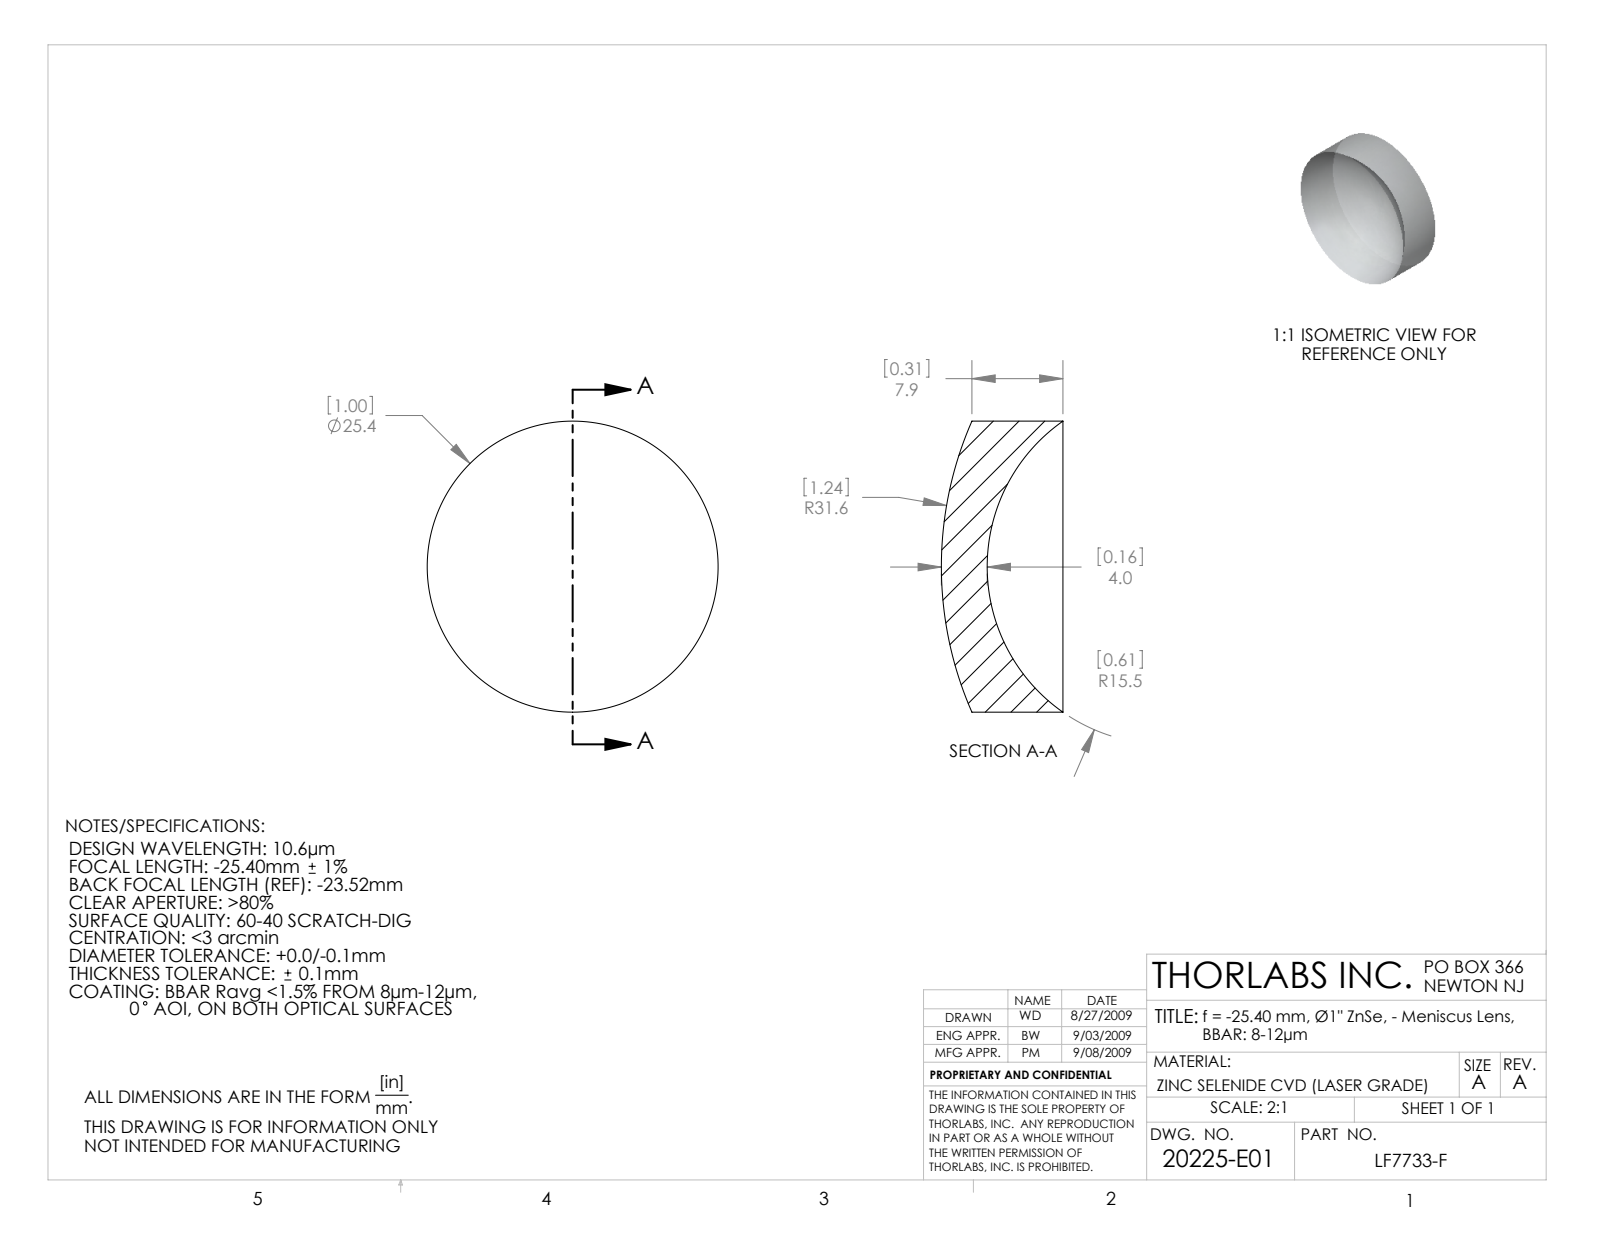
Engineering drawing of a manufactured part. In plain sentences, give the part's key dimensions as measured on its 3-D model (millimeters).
The part is named "20225-E0W". Its 3-D file was written by "SolidWorks 2007 (CONFIG_CONTROL_DESIGN)". It is 1 solid with 6 faces: 0 planar, 2 cylindrical and 4 other. Overall it measures 25.4 by 25.4 by 10.61 millimeters. Its volume is 2 885 cubic millimeters and its surface area 1 807 square millimeters. Round bosses or shafts: 1 of diameter 25.4.
